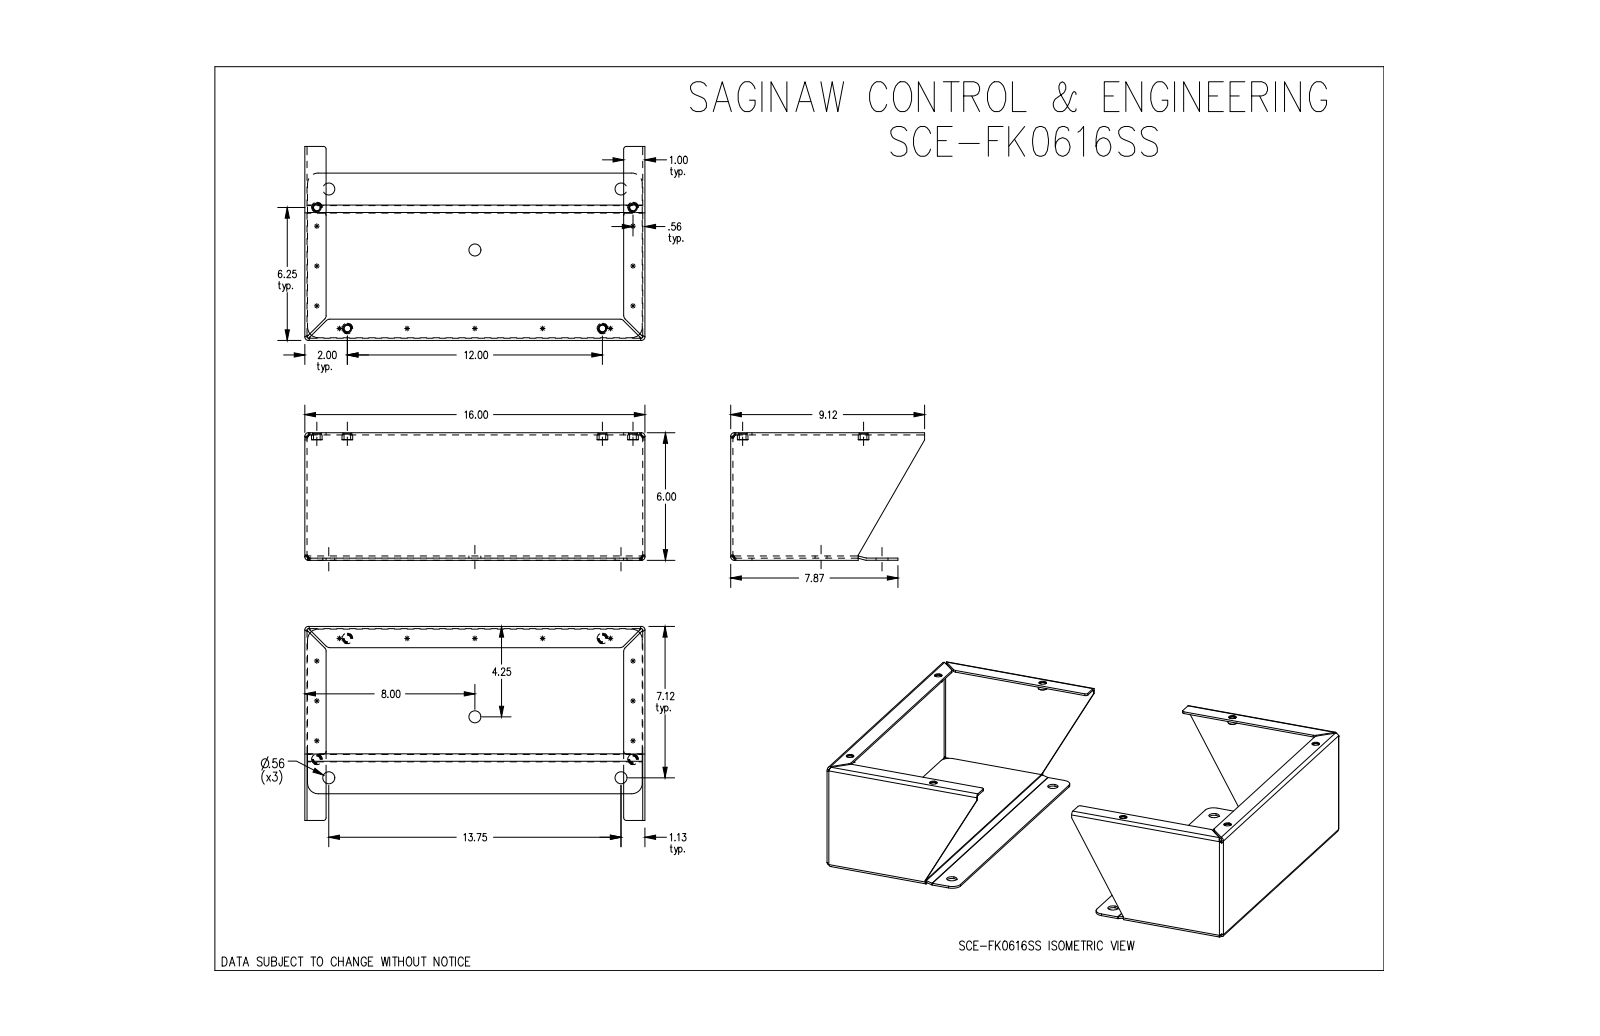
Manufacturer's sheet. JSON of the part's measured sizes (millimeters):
{"part_name": "SCE-FK0616SS", "step_written_by": "SolidWorks 2019 (CONFIG_CONTROL_DESIGN)", "units": "millimeters", "bodies": {"solids": 12, "faces": 286, "planar": 120, "cylindrical": 110, "other": 56}, "overall_size": [609.6, 406.4, 152.4], "volume_mm3": 1210000, "surface_area_mm2": 936800, "round_holes": [[7.9, 8], [10.5, 8], [14.3, 6]], "round_bosses_or_shafts": [[12.7, 8], [10.5, 8]], "partial_cylinders_radius": [[4.2, 16], [1.6, 14], [3.2, 8], [5.6, 8], [12.7, 8], [1.6, 2]], "face_to_face_distances": [2.6, 607, 403.8, 147.1, 149.8, 2.6, 149.7, 609.6, 604.3, 401.1], "hole_center_spacings": [26.3, 149, 168, 178.9, 189.2, 195.6, 270.4, 365.3]}
